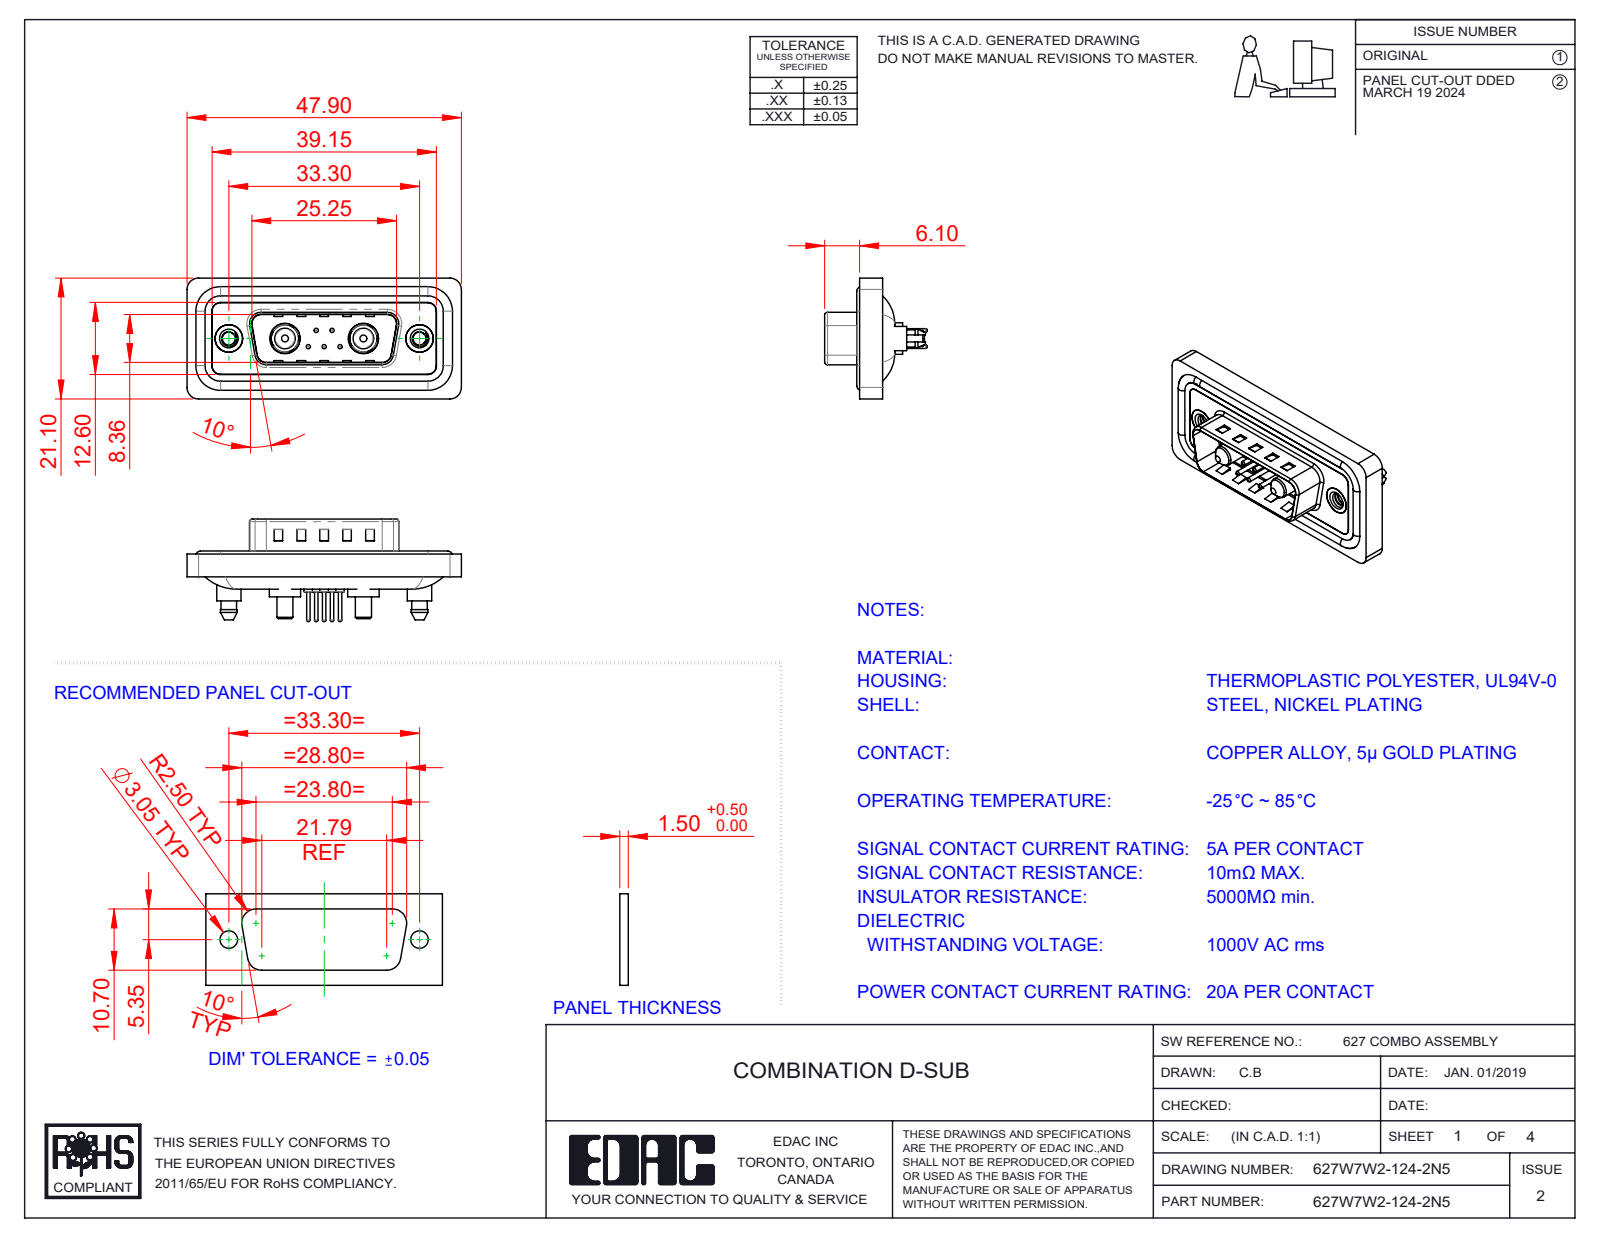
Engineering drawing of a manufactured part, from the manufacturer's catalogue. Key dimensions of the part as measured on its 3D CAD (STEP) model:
Part name (STEP PRODUCT): 627Combo Shell Front_15 Contacts; Power Pin_20A S; 627Combo Contact Row 1_24; 627Combo Waterproof Housing_15 Contacts (+5 more)
STEP written by: SolidWorks 2023 (CONFIG_CONTROL_DESIGN)
Units: millimetres
Bodies: 16 solids, 760 faces (248 planar, 324 cylindrical, 188 other)
Overall size (bounding box): 47.9 × 21.1 × 17.9
Volume: 5 650 mm³ · Surface area: 9 126 mm²
Round holes (diameter × count): ⌀0.75 ×5, ⌀1.6 ×5, ⌀2 ×5, ⌀2.26 ×2, ⌀4 ×2, ⌀4.8 ×2, ⌀4.85 ×2, ⌀5 ×2, ⌀5.3 ×2
Round bosses / shafts (diameter × count): ⌀1.5 ×5, ⌀0.6 ×5, ⌀1.6 ×4, ⌀5.5 ×2, ⌀5.4 ×2, ⌀5.2 ×2, ⌀4.9 ×2, ⌀4.75 ×2
Partial cylindrical surfaces — rounded edges, fillets, slot ends (radius × count): R1.5 ×28, R2 ×20, R1.6 ×10, R0.5 ×8, R0.25 ×4, R0.6 ×4, R0.65 ×4, R0.9 ×4
Main face-to-face distances: 0.4, 1.1, 1.5, 1.6, 0.5, 3.1, 2.9, 4, 0.7, 0.82
Hole centre spacings: 3.16, 2.77, 9.8, 23.5, 4.31, 4.33, 5.03, 5.04
